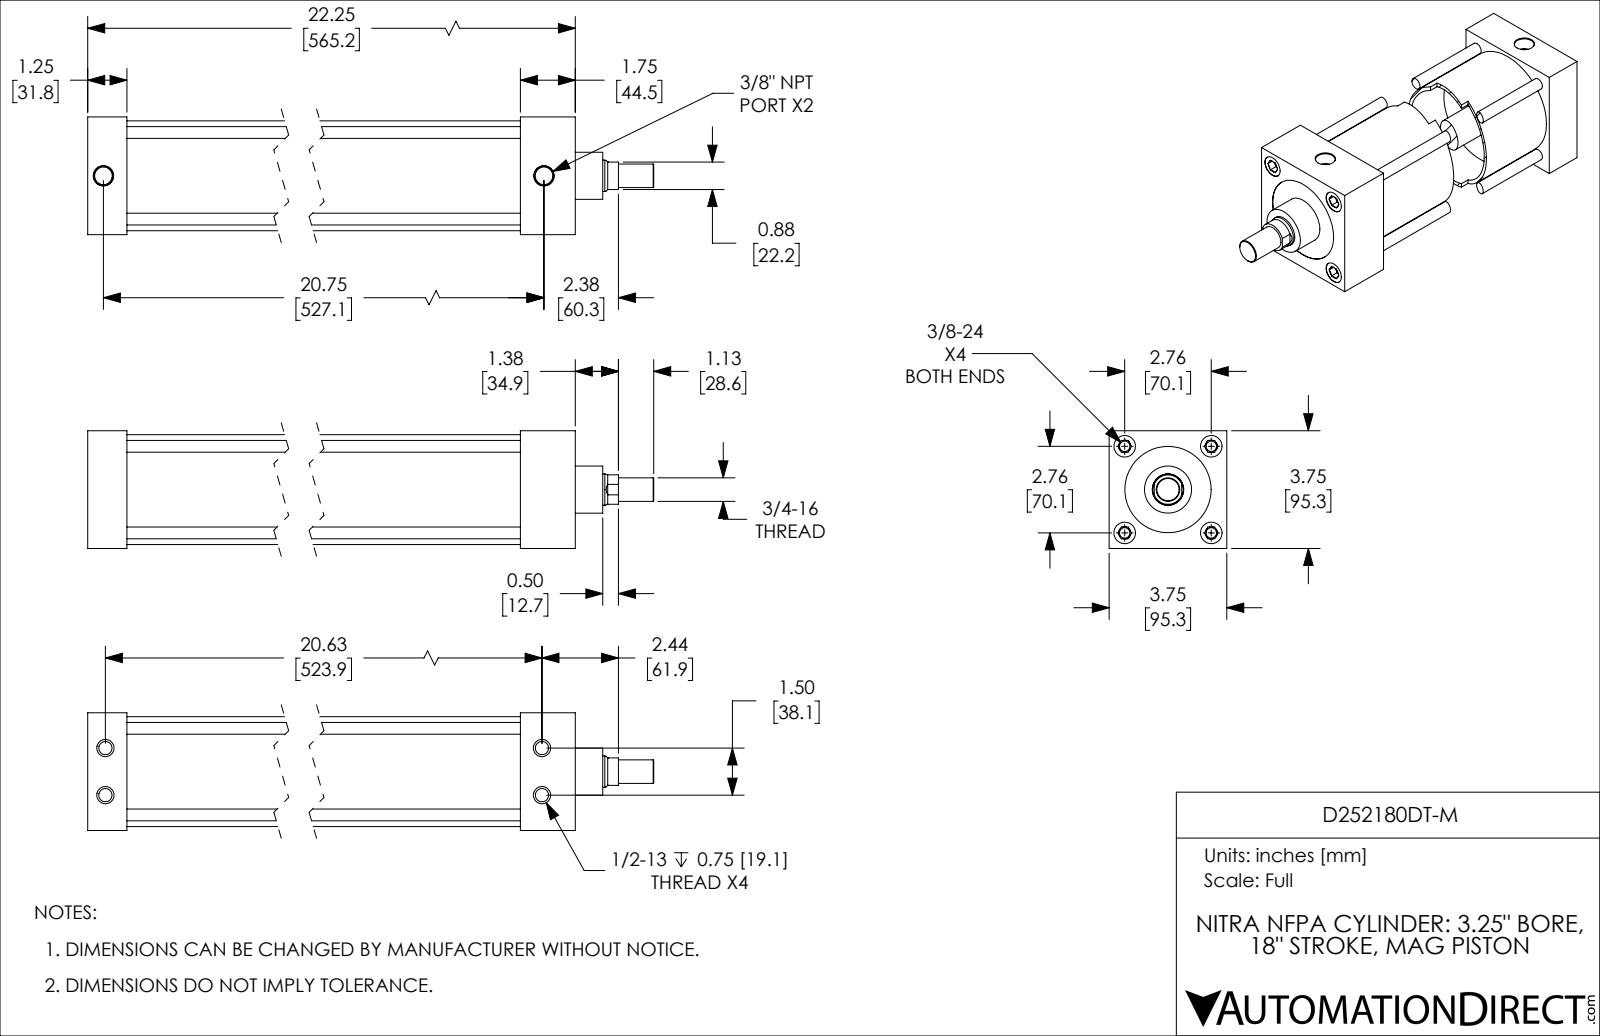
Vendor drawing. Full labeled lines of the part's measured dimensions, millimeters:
Part name (STEP PRODUCT): D252180DT-M_PISTON_KK1; D252180DT-M_BODY; D252180DT-M
STEP written by: SolidWorks 2019 (CONFIG_CONTROL_DESIGN)
Units: millimetres
Bodies: 2 solids, 198 faces (58 planar, 62 cylindrical, 78 other)
Overall size (bounding box): 628.7 × 95.3 × 95.3
Volume: 1 653 000 mm³ · Surface area: 467 400 mm²
Round holes (diameter × count): ⌀8.4 ×4, ⌀10.7 ×4, ⌀17.4 ×4, ⌀14.3 ×2, ⌀25.4 ×1, ⌀69.9 ×1, ⌀82.6 ×1
Round bosses / shafts (diameter × count): ⌀9.5 ×4, ⌀88.9 ×1, ⌀82.5 ×1, ⌀38.1 ×1, ⌀25.4 ×1, ⌀19.1 ×1
Partial cylindrical surfaces — rounded edges, fillets, slot ends (radius × count): R11.9 ×1
Main face-to-face distances: 31.8, 95.3, 520.7, 489, 63.5, 457.2, 565.2, 533.4, 501.7, 44.5
Hole centre spacings: 19.1, 49.6, 70.1, 525.8, 38.1, 99.1, 523.9, 525.2
